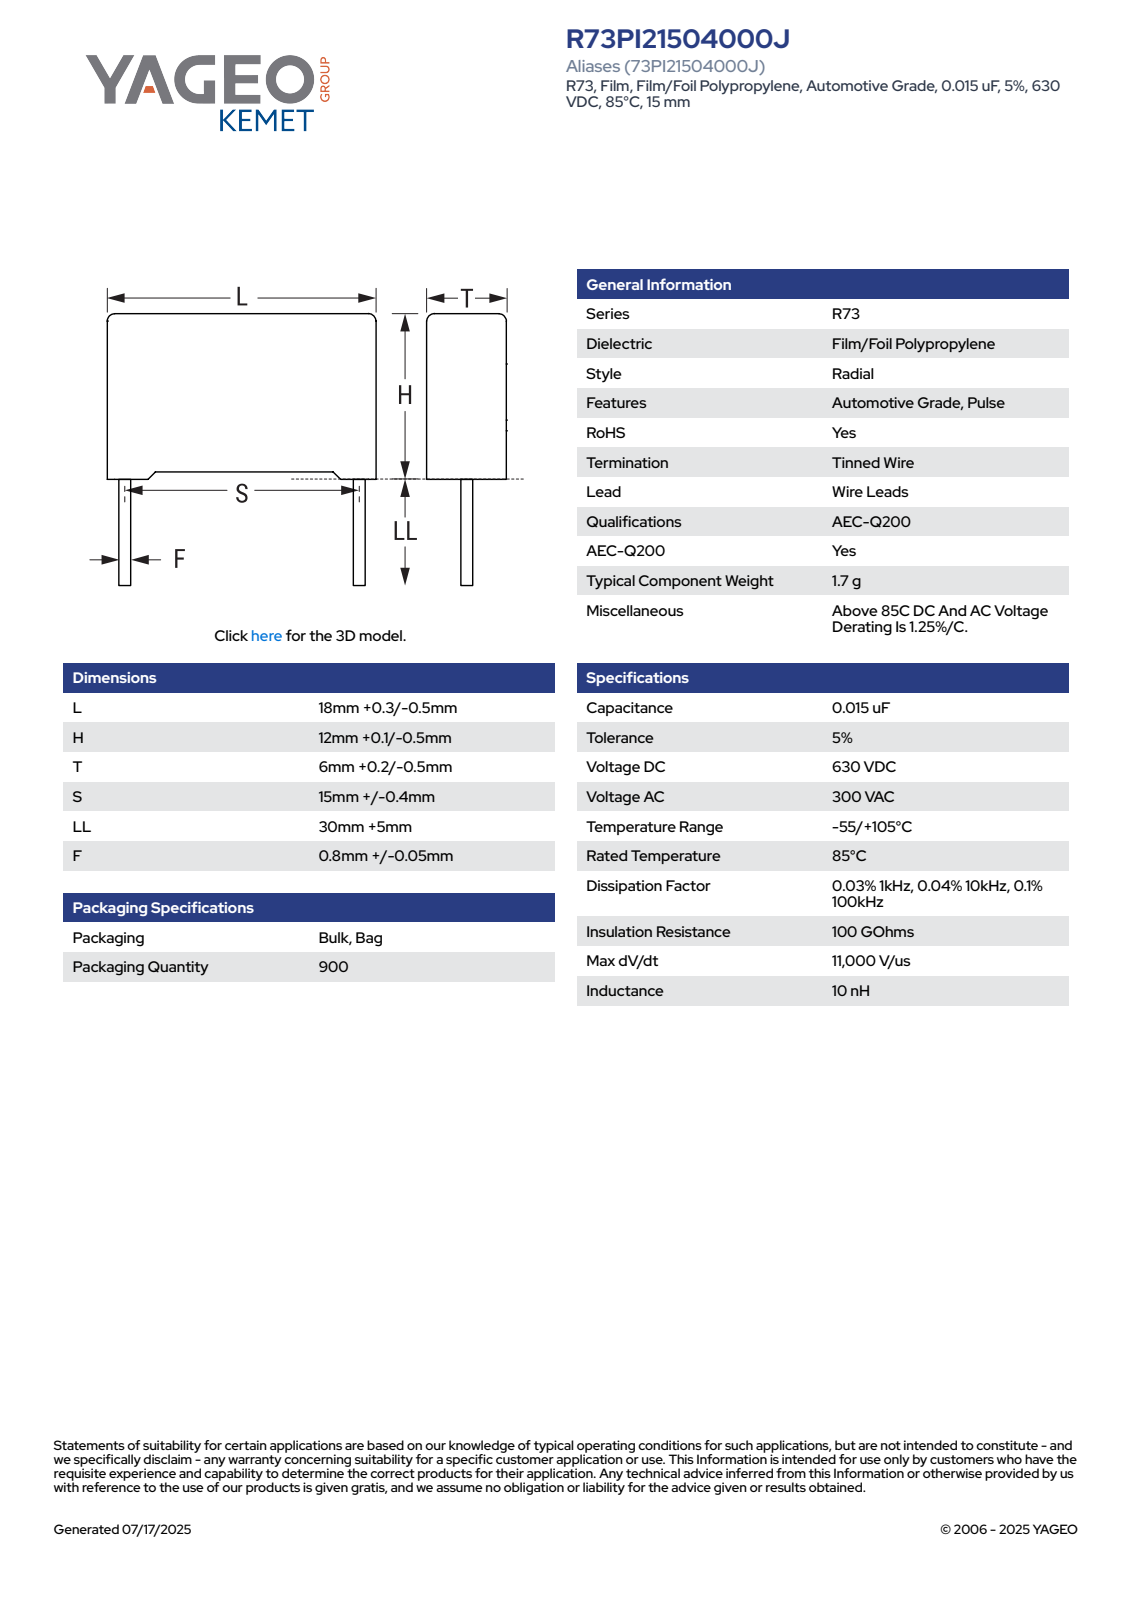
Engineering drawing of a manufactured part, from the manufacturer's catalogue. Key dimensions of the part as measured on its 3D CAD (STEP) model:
Part name (STEP PRODUCT): CFR_RB2_18X12X6_L18.3H12.1T6.2S15LL35F0.85
STEP written by: SolidWorks 2021 (AUTOMOTIVE_DESIGN)
Units: millimetres
Bodies: 4 solids, 85 faces (77 planar, 8 cylindrical, 0 other)
Overall size (bounding box): 47.1 × 18.3 × 6.21
Volume: 1 341 mm³ · Surface area: 1 040 mm²
Round bosses / shafts (diameter × count): ⌀0.85 ×2
Partial cylindrical surfaces — rounded edges, fillets, slot ends (radius × count): R0.5 ×4
Main face-to-face distances: 6.2, 11.35, 18.3, 0.61, 5.59, 0.75, 12.1, 0.42, 0.33, 11.68
